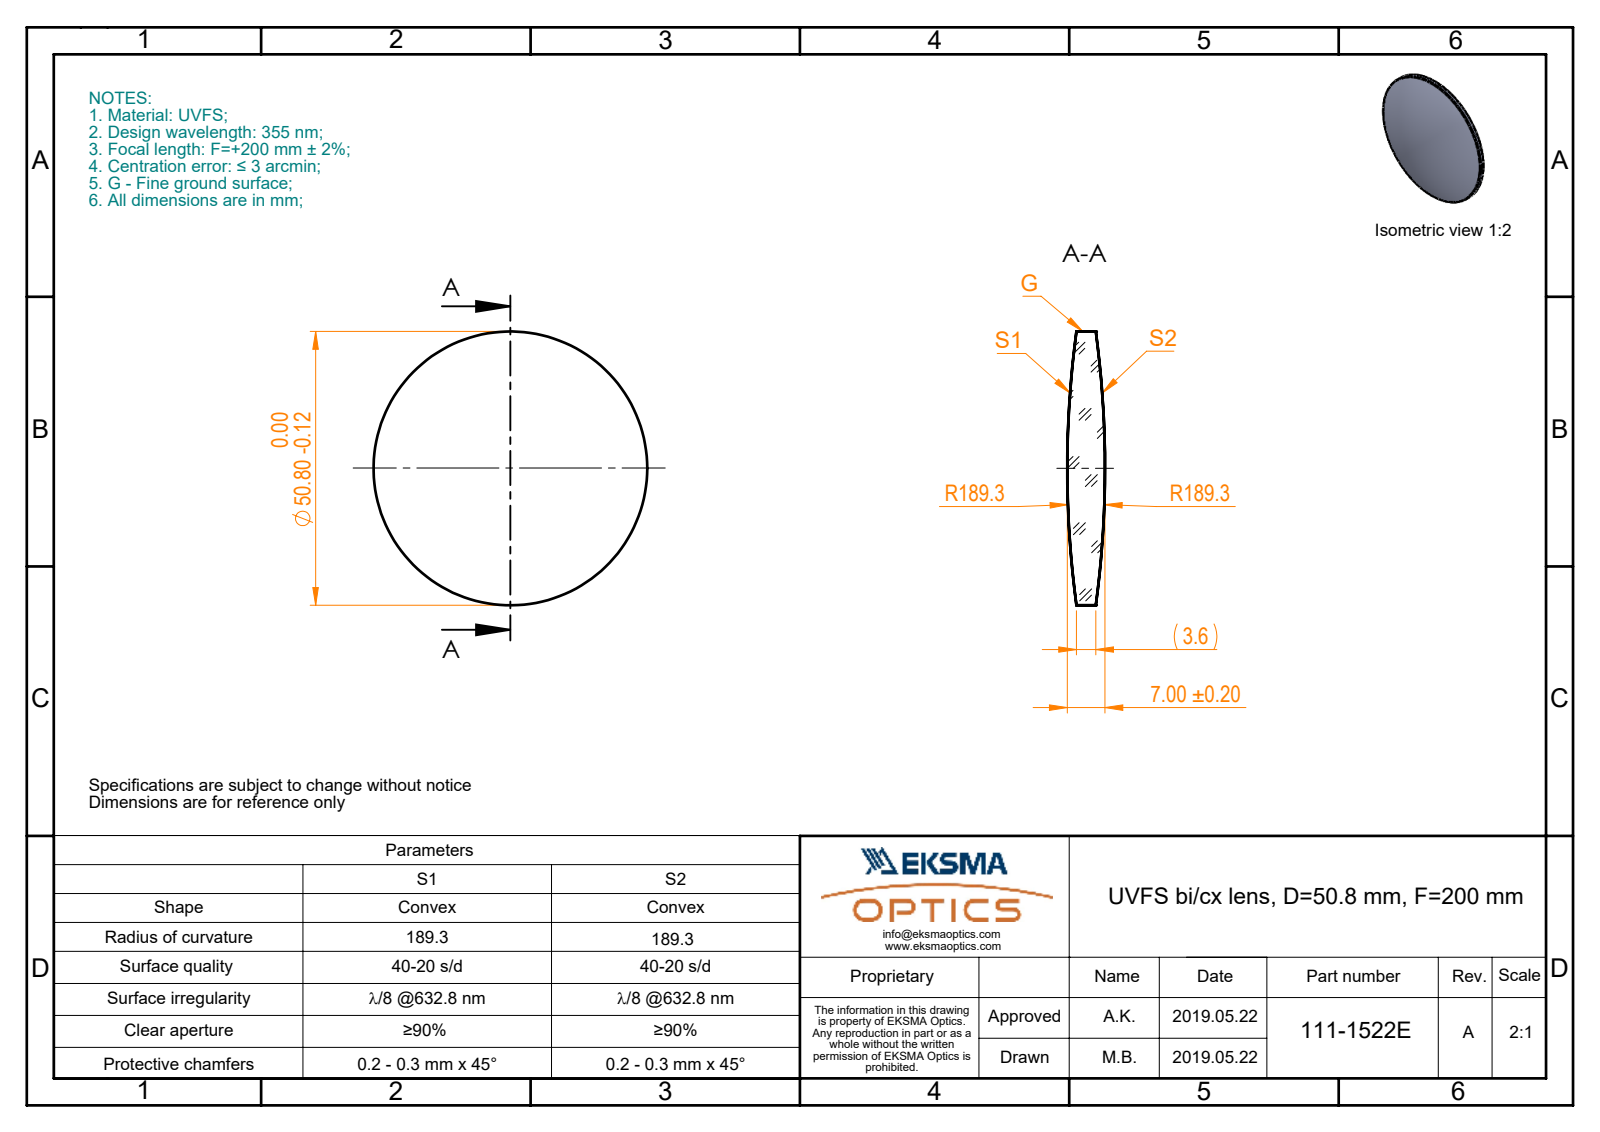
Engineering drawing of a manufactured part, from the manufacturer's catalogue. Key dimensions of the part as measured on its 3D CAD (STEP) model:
Part name (STEP PRODUCT): 111-1522E UVFS bi-cx 50.8 F200
STEP written by: SolidWorks 2017 (CONFIG_CONTROL_DESIGN)
Units: millimetres
Bodies: 1 solid, 6 faces (0 planar, 2 cylindrical, 4 other)
Overall size (bounding box): 50.8 × 50.8 × 7
Volume: 10 724 mm³ · Surface area: 4 643 mm²
Round bosses / shafts (diameter × count): ⌀50.8 ×1
